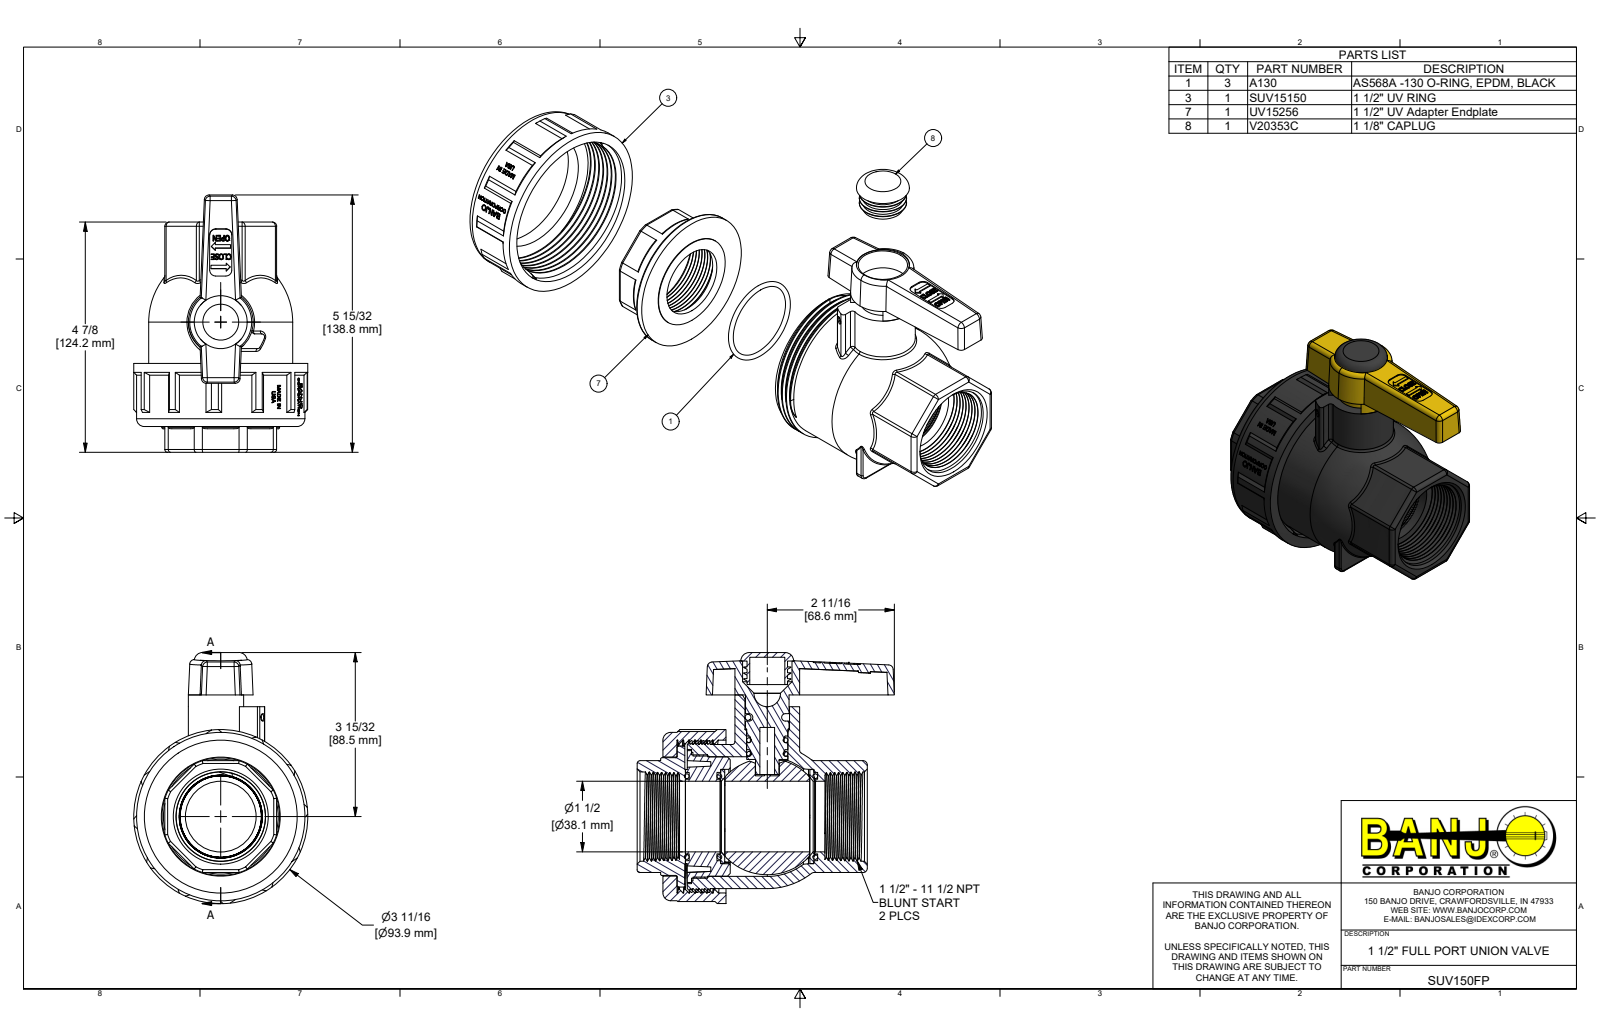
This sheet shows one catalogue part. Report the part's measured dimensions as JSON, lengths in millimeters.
{"part_name": "SUV150FP; SUV15254; SUV15153; SUV15150 (+8 more)", "step_written_by": "Autodesk Inventor 2022 (AUTOMOTIVE_DESIGN)", "units": "millimeters", "bodies": {"solids": 15, "faces": 1150, "planar": 502, "cylindrical": 213, "other": 435}, "overall_size": [138.8, 135.4, 93.9], "volume_mm3": 408000, "surface_area_mm2": 166100, "round_holes": [[8, 1], [14.3, 1], [18.9, 1], [22.3, 1], [24.1, 1], [26.7, 1], [28.6, 1], [38.1, 1], [47.6, 1], [47.6, 1], [51, 1], [64.3, 1]], "round_bosses_or_shafts": [[93.9, 1], [90.9, 1], [81.9, 1], [77.7, 1], [76.1, 1], [71.1, 1], [66.5, 1], [64.4, 1]], "partial_cylinders_radius": [[2.3, 16], [1.5, 11], [2.5, 10], [0.8, 6], [3.2, 6], [21.5, 4], [13.7, 1], [25.1, 1]], "face_to_face_distances": [4.2, 60.3, 1.3, 11.8, 7.6, 22.2, 5.5, 13.1, 1, 2]}
